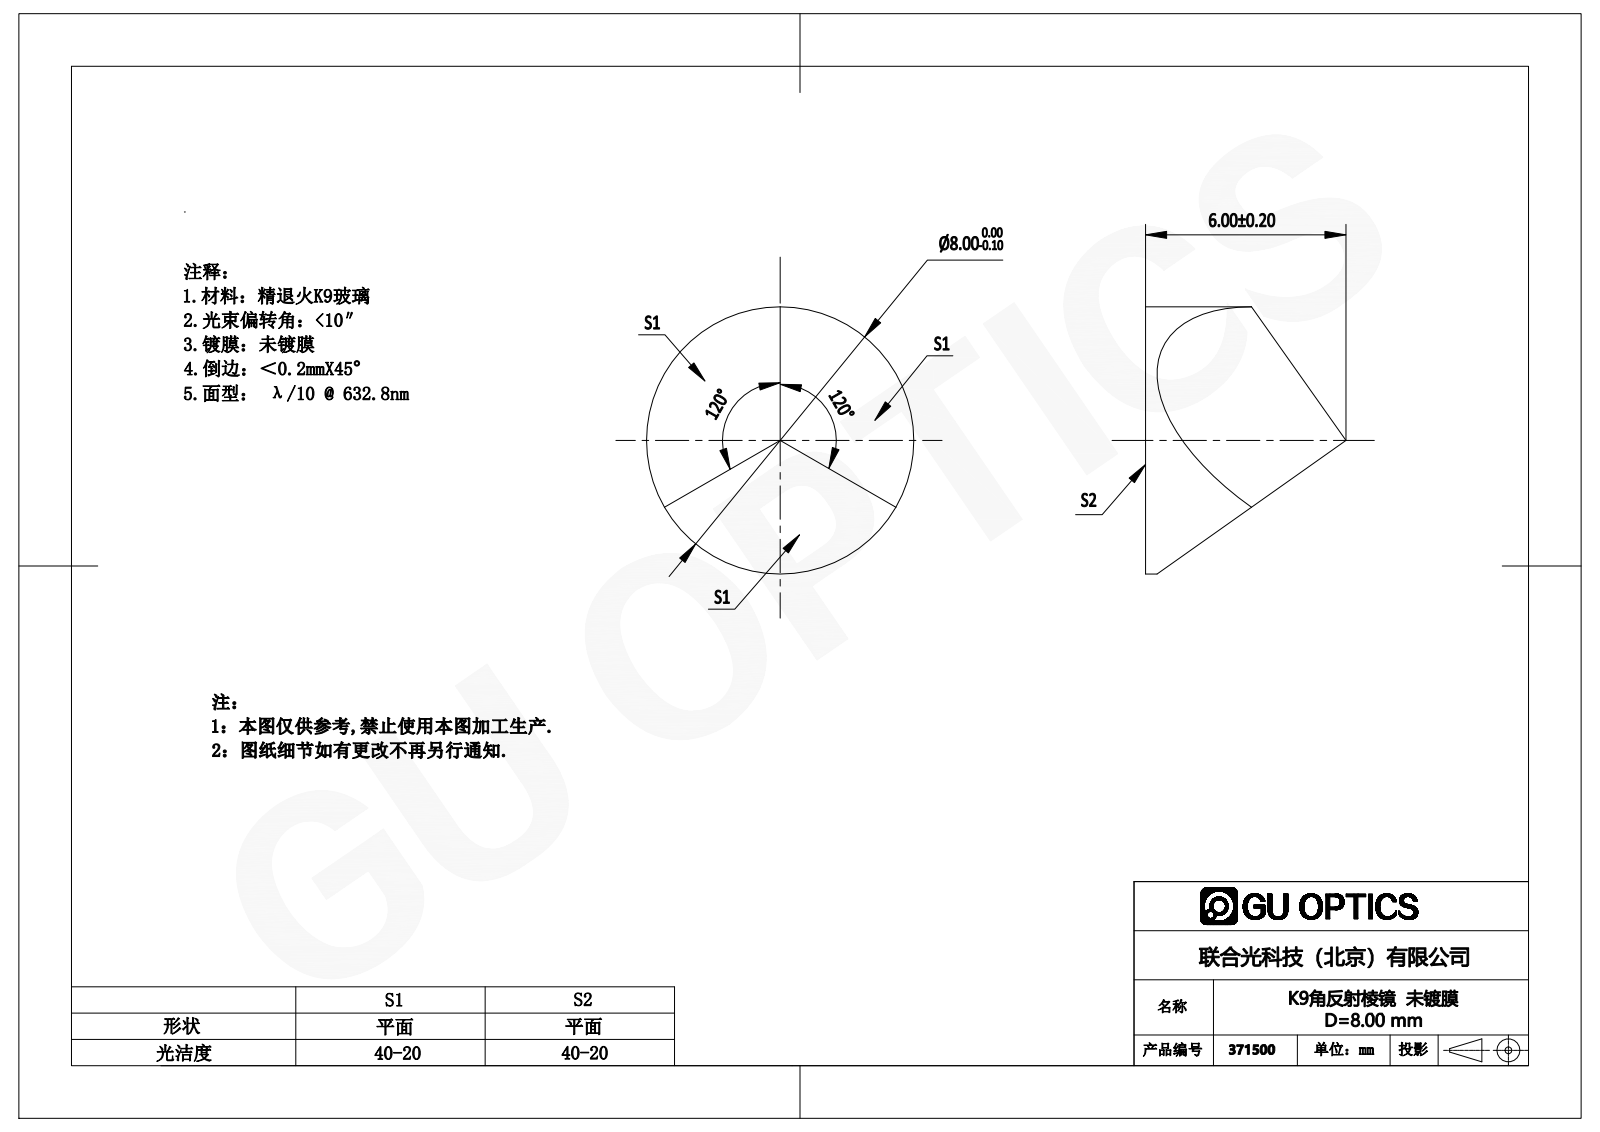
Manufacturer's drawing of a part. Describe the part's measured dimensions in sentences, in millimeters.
The part is named "371500". Its 3-D file was written by "SolidWorks 2020 (CONFIG_CONTROL_DESIGN)". It is 1 solid with 5 faces: 4 planar, 1 cylindrical and 0 other. Overall it measures 8 by 8 by 6 millimeters. Its volume is 145 cubic millimeters and its surface area 170 square millimeters. Round bosses or shafts: 1 of diameter 8.
